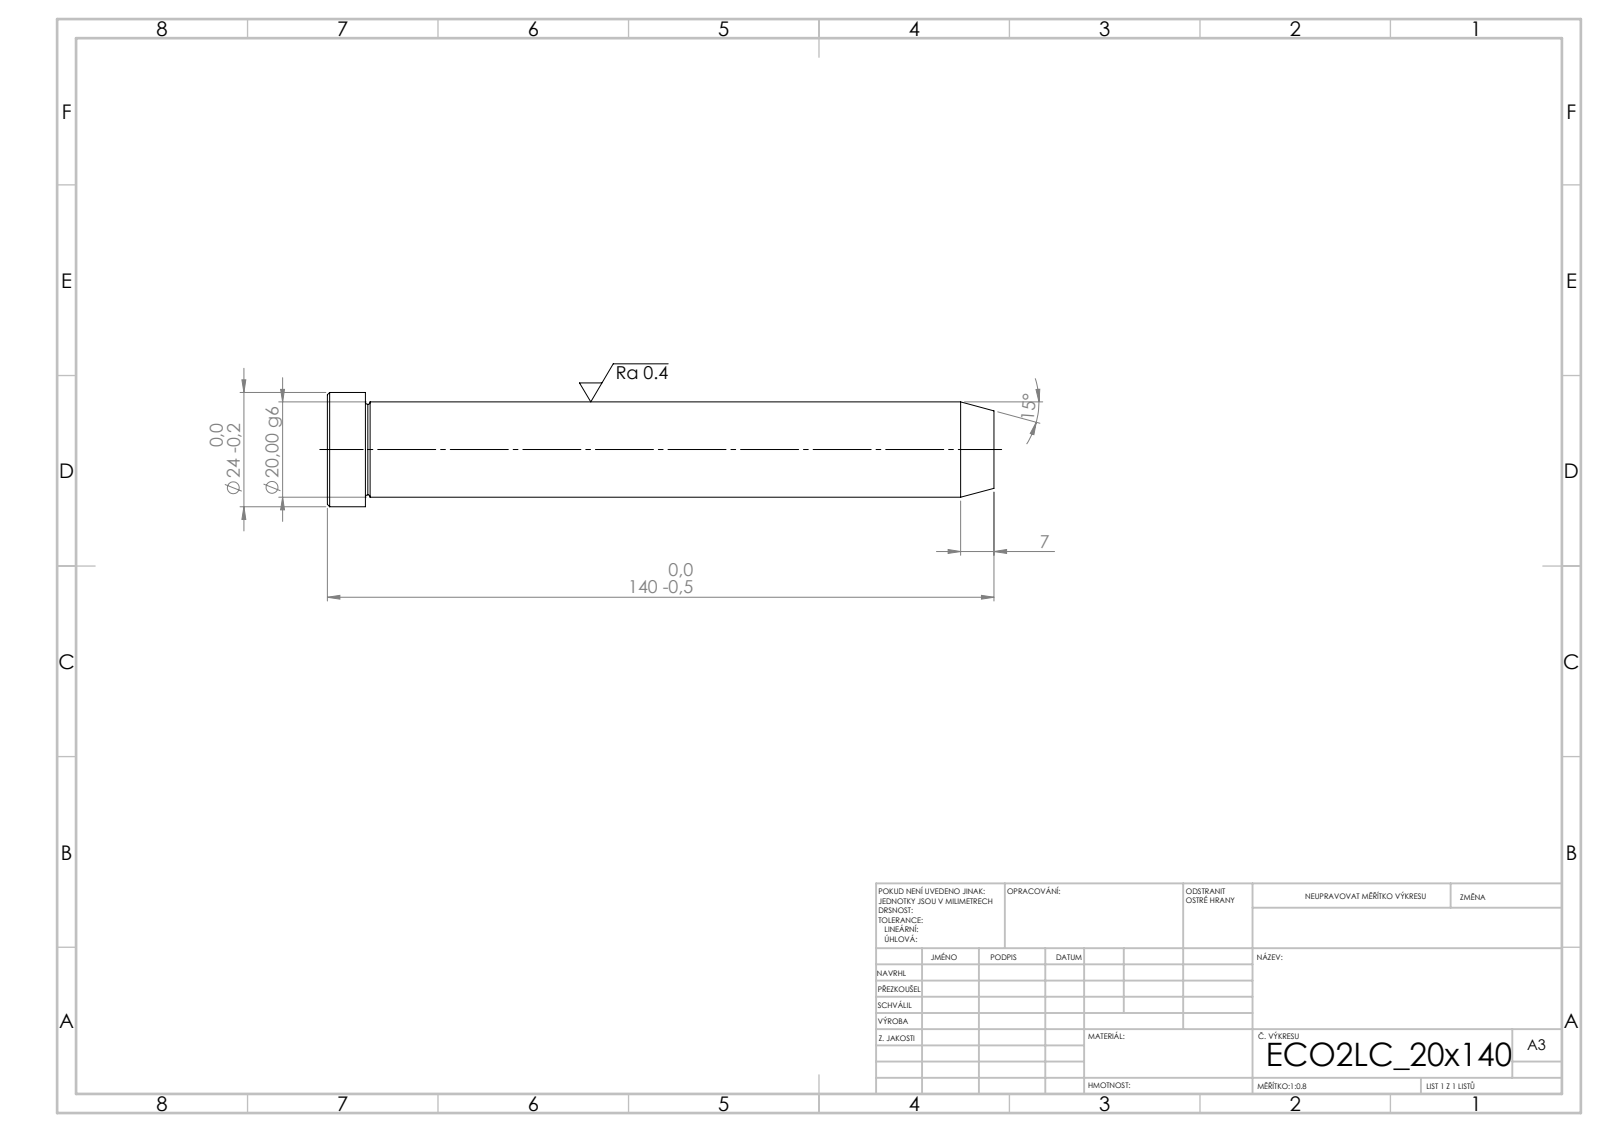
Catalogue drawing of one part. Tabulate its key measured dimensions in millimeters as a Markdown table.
| quantity | value |
| --- | --- |
| STEP written by | SolidWorks 2019 (CONFIG_CONTROL_DESIGN) |
| units | millimeters |
| bodies | 1 solid, 15 faces (3 planar, 4 cylindrical, 8 other) |
| overall size | 140 × 24 × 24 |
| volume | 44 668 mm³ |
| surface area | 9 678 mm² |
| round bosses / shafts (diameter × count) | 24 × 1, 20 × 1 |
| main face-to-face distances | 140, 132, 8 |
